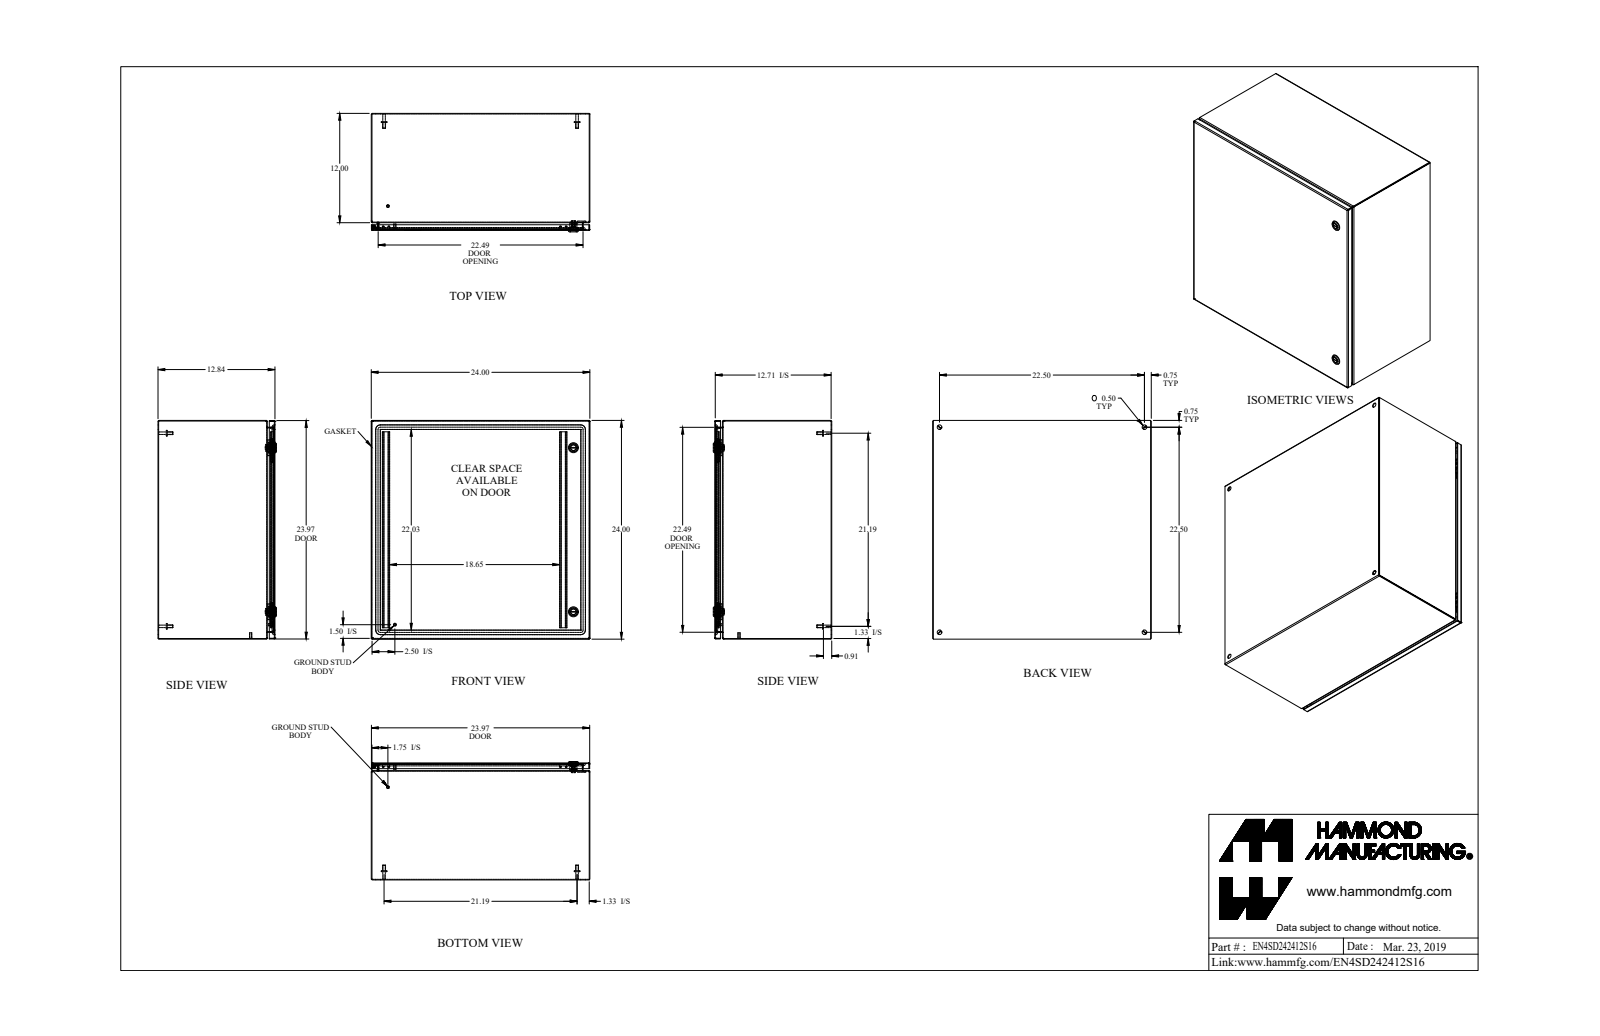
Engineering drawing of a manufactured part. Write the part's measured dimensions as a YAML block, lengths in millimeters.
part_name: "EN4SD242412S16"
step_written_by: "SolidWorks 2019 (AUTOMOTIVE_DESIGN)"
units: millimeters
bodies: {solids: 31, faces: 773, planar: 383, cylindrical: 258, other: 132}
overall_size: [609.6, 609.6, 330.3]
volume: 3135000
surface_area: 3463000
round_holes:
  - {diameter: 12.7, count: 6}
  - {diameter: 5, count: 2}
  - {diameter: 9.8, count: 2}
  - {diameter: 16, count: 2}
  - {diameter: 19.5, count: 2}
  - {diameter: 4.4, count: 1}
  - {diameter: 6.1, count: 1}
  - {diameter: 6.1, count: 1}
round_bosses_or_shafts:
  - {diameter: 15.9, count: 6}
  - {diameter: 8, count: 6}
  - {diameter: 7, count: 4}
  - {diameter: 27.9, count: 2}
  - {diameter: 19.9, count: 2}
  - {diameter: 13.3, count: 2}
  - {diameter: 6.4, count: 2}
  - {diameter: 6, count: 2}
partial_cylinders:
  - {radius: 0.9, count: 14}
  - {radius: 2.7, count: 14}
  - {radius: 0.3, count: 12}
  - {radius: 1.2, count: 12}
  - {radius: 7.9, count: 12}
  - {radius: 2.5, count: 8}
  - {radius: 0.2, count: 4}
  - {radius: 1.6, count: 4}
face_to_face_distances: [1.8, 324.4, 607.8, 322.5, 605.9, 326.2, 609.6, 21.4, 303, 19.1]
hole_center_spacings: [571.5, 63.2, 515.1, 547.5, 749.1, 808.2, 457.2]
